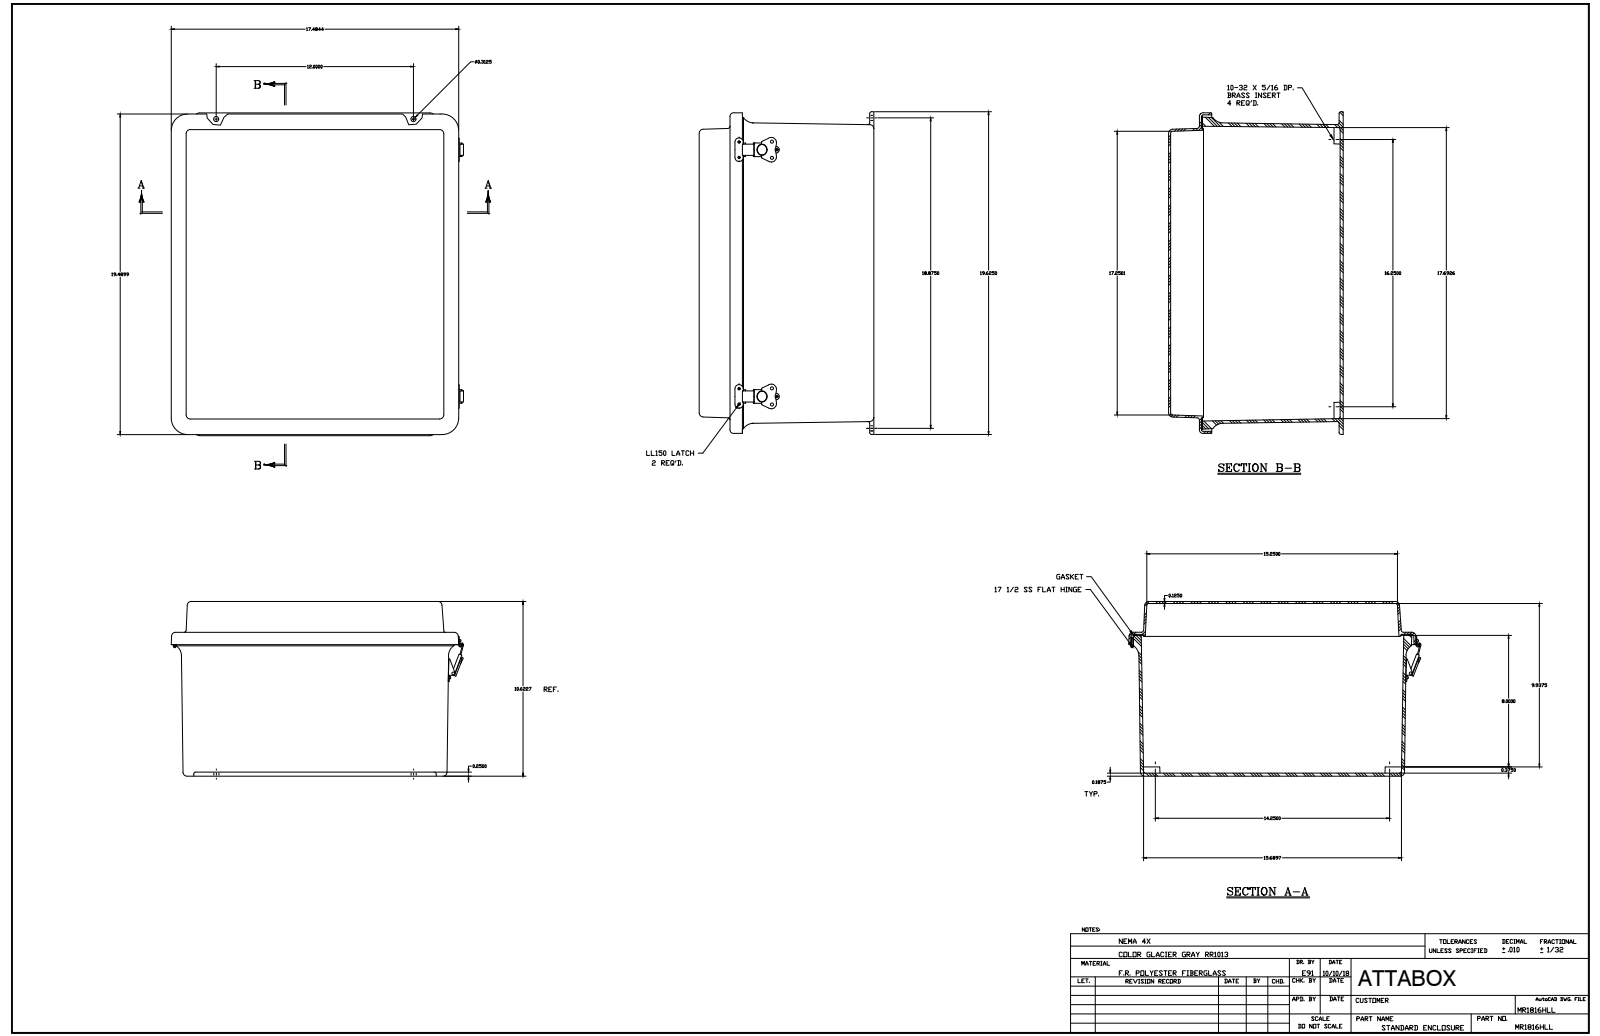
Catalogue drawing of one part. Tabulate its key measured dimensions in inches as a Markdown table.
| quantity | value |
| --- | --- |
| part name | MR1816HLL |
| STEP written by | SolidWorks 2018 (AUTOMOTIVE_DESIGN) |
| units | inches |
| bodies | 52 solids, 1362 faces (616 planar, 527 cylindrical, 219 other) |
| overall size | 19.625 × 17.703 × 10.642 |
| volume | 249.6 in³ |
| surface area | 2 947 in² |
| round holes (diameter × count) | 0.14 × 20, 0.131 × 12, 0.152 × 5, 0.13 × 4, 0.156 × 4, 0.165 × 4, 0.197 × 4, 0.218 × 4, 0.118 × 2, 0.138 × 2, 0.181 × 2, 0.182 × 2 |
| round bosses / shafts (diameter × count) | 0.25 × 20, 0.125 × 11, 0.125 × 9, 0.27 × 4, 0.583 × 2, 0.524 × 2, 0.209 × 2, 0.185 × 2 |
| partial cylindrical surfaces (radius × count) | 0.031 × 20, 0.125 × 20, 0.079 × 19, 0.25 × 12, 0.037 × 8, 0.039 × 8, 0.045 × 8, 0.047 × 8 |
| main face-to-face distances | 0.187, 0.188, 0.125, 10.517, 10.329, 10.642, 10.454, 2, 0.125, 8.642 |
| hole center spacings | 3.375, 3.375, 6.75, 14.984, 10.25, 14.984, 0.25, 9.75 |
